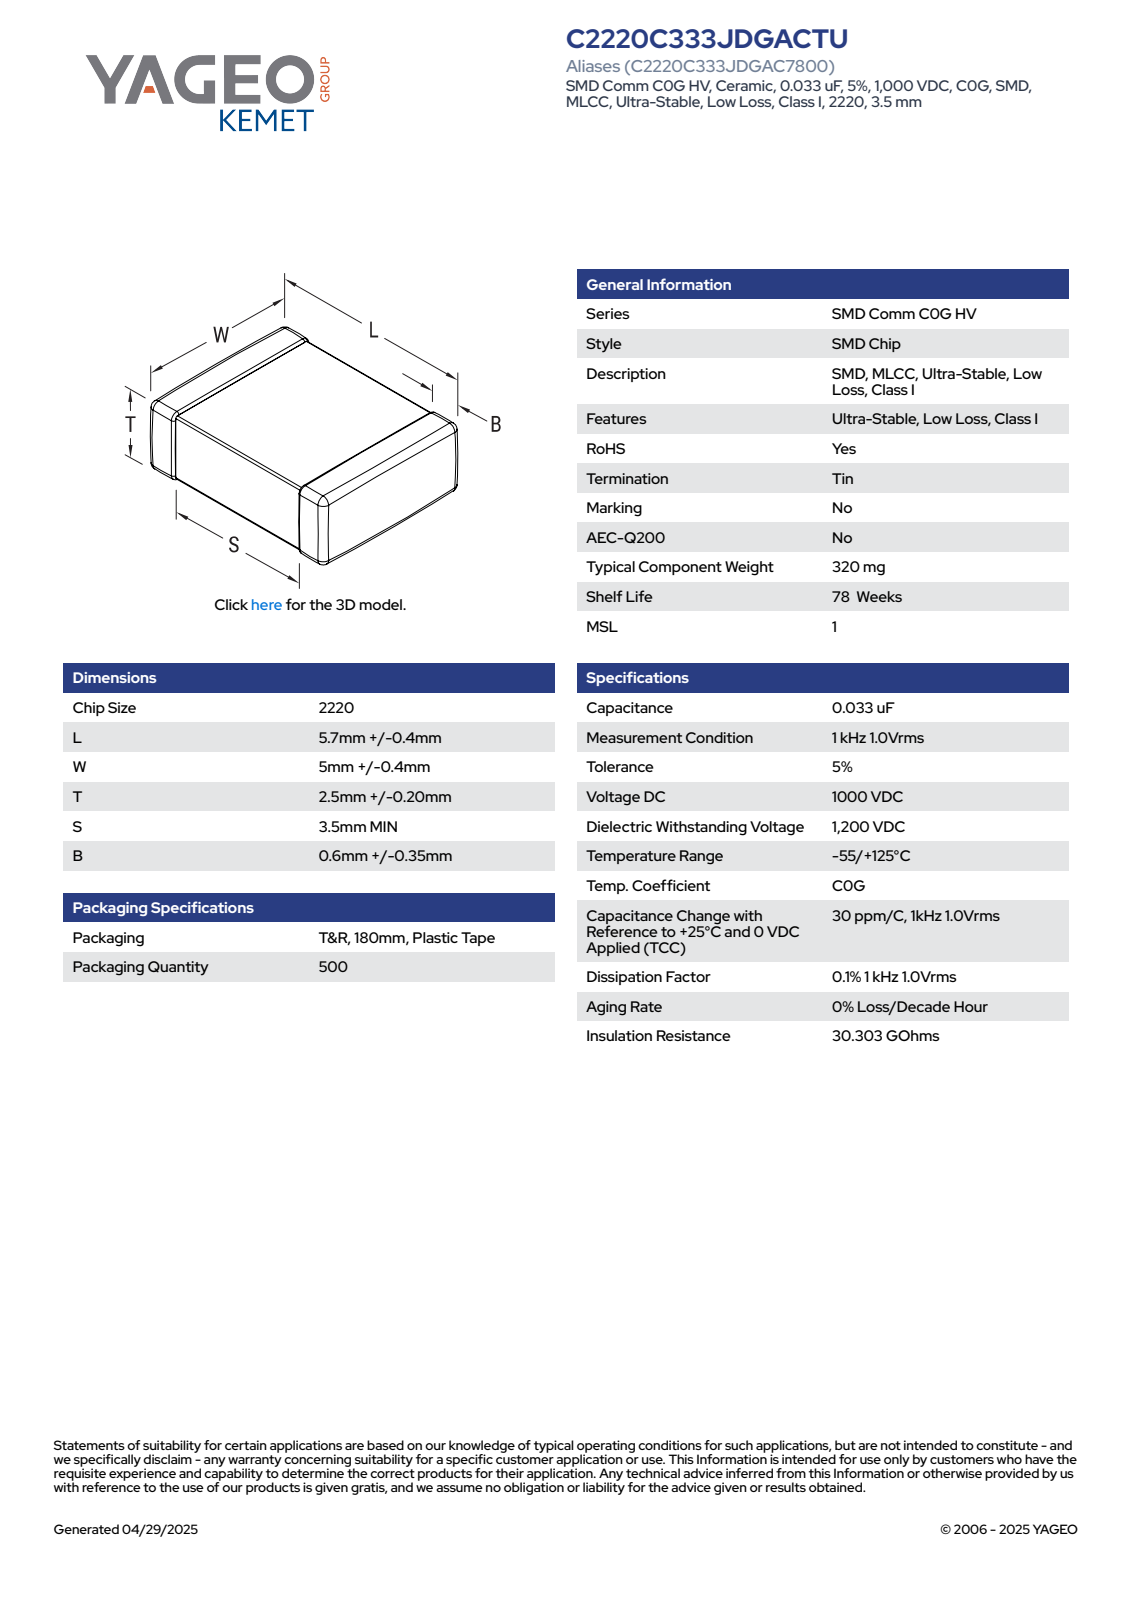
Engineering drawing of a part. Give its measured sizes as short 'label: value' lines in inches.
name: CCS_CCSTD_2220_L6.1W5.4T2.7B0.6
written by: SolidWorks 2021 (AUTOMOTIVE_DESIGN)
unit: in
bodies: 4 solids, 125 faces (71 planar, 38 cylindrical, 16 other)
size: 0.24 × 0.213 × 0.106
volume: 0.005 in³; area: 0.197 in²
rounds: 24× R0.004
face distances: 0.098, 0.102, 0.24, 0.204, 0.106, 0.208, 0.213, 0.098, 0.142, 0.13
